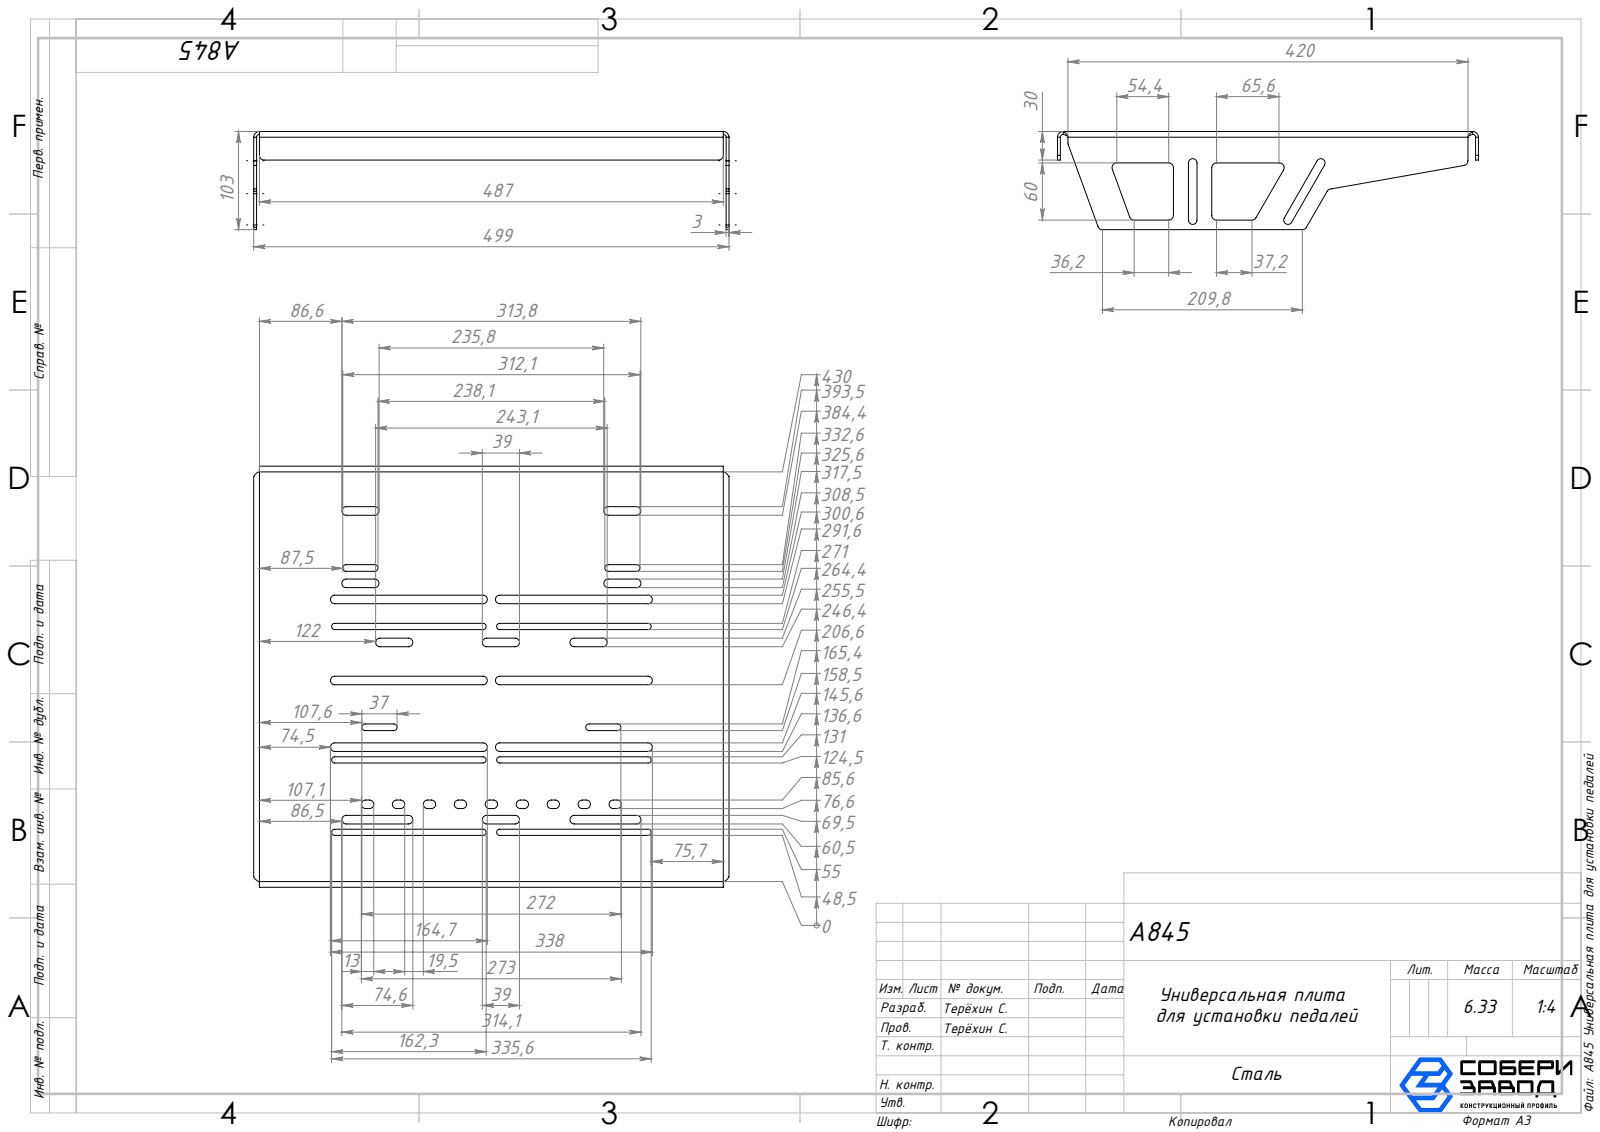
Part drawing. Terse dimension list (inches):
name: A845 Универсальная плита для установки педалей
written by: SolidWorks 2025 (AUTOMOTIVE_DESIGN)
unit: in
bodies: 1 solid, 296 faces (128 planar, 164 cylindrical, 4 other)
size: 19.647 × 17.4 × 4.056
volume: 49.21 in³; area: 878.1 in²
rounds: 30× R0.176, 20× R0.178, 8× R0.137, 6× R0.177, 6× R0.197, 4× R0.118, 4× R0.128, 4× R0.128
face distances: 0.118, 19.529, 17.282, 19.411, 19.647, 17.4, 17.164, 1.063, 1.181, 0.353
